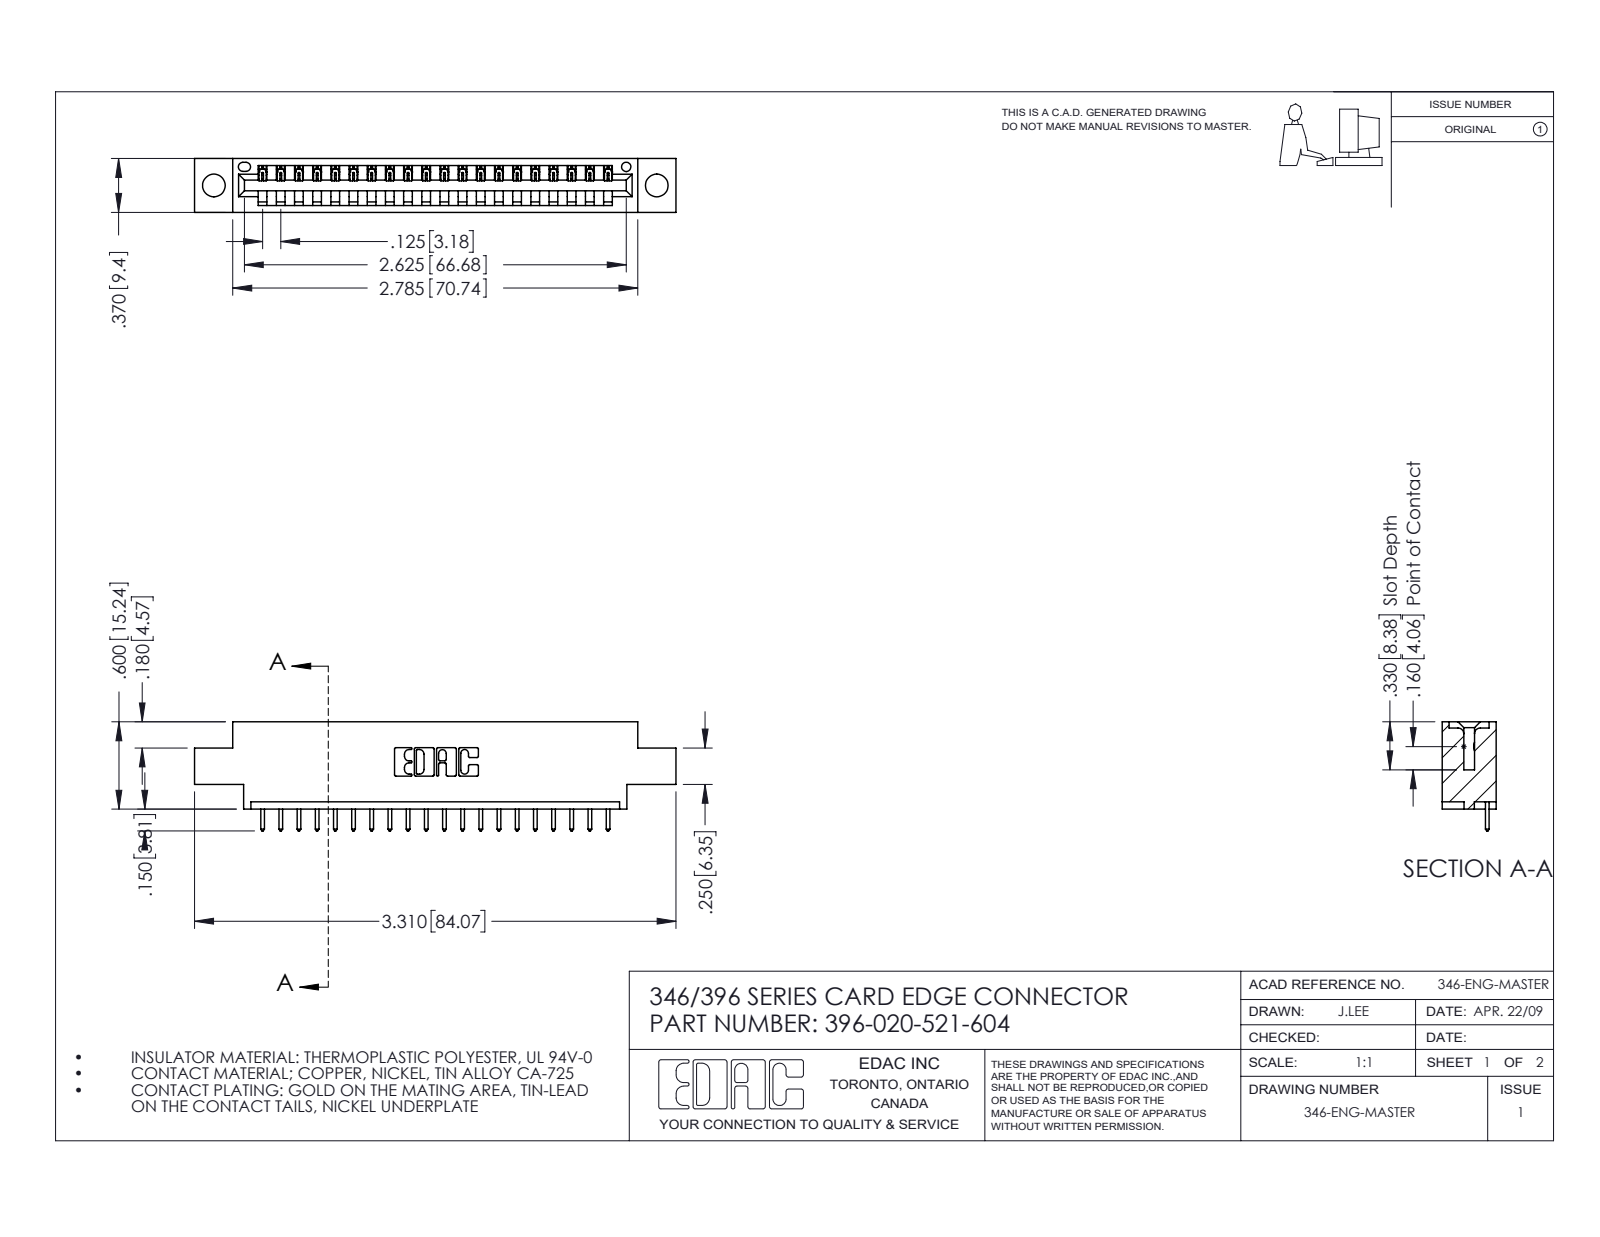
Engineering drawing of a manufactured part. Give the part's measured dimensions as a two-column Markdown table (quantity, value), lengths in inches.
| quantity | value |
| --- | --- |
| part name | 396-020-521-604; 345-292-001_345-293-121; 346 Part_0.170 Offset - 0.156 Dia-TH |
| STEP written by | SolidWorks 2016 (CONFIG_CONTROL_DESIGN) |
| units | inches |
| bodies | 21 solids, 1286 faces (880 planar, 406 cylindrical, 0 other) |
| overall size | 3.31 × 0.75 × 0.37 |
| volume | 0.464 in³ |
| surface area | 13.94 in² |
| round holes (diameter × count) | 0.156 × 2, 0.064 × 1 |
| partial cylindrical surfaces (radius × count) | 0.006 × 40, 0.01 × 40, 0.01 × 22, 0.007 × 6, 0.031 × 6, 0.026 × 3, 0.031 × 2, 0.04 × 2 |
| main face-to-face distances | 0.048, 0.322, 0.37, 0.25, 0.072, 0.298, 0.025, 0.148, 0.222, 0.1 |
| hole center spacings | 0.246, 2.837, 3.045 |
